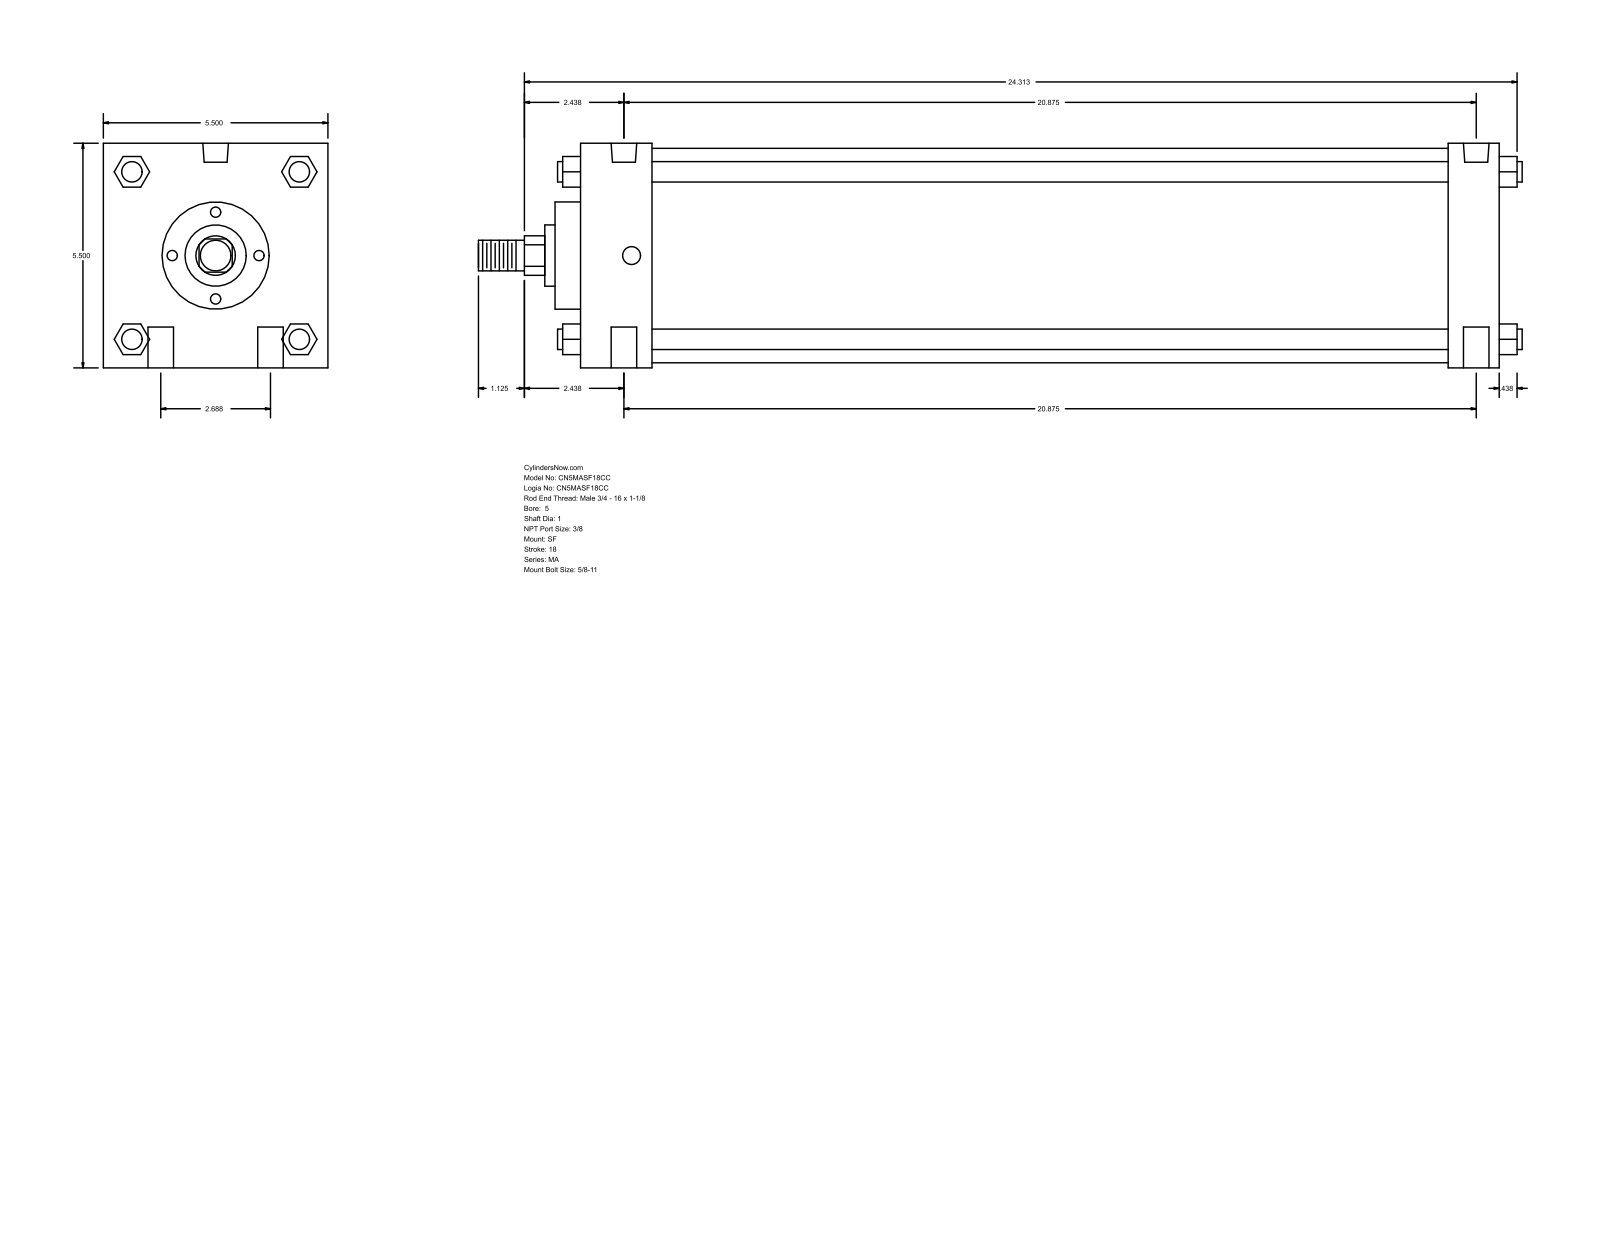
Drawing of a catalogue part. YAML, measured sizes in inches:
part_name: "MA_SF__0500_1"
step_written_by: "GSSL Pune (CONFIG_CONTROL_DESIGN)"
units: inches
bodies: {solids: 0, faces: 126, planar: 95, cylindrical: 31, other: 0}
overall_size: [25.563, 5.5, 5.5]
round_holes:
  - {diameter: 0.625, count: 4}
  - {diameter: 0.437, count: 2}
  - {diameter: 0.627, count: 2}
round_bosses_or_shafts:
  - {diameter: 0.5, count: 4}
  - {diameter: 5.25, count: 1}
  - {diameter: 2.625, count: 1}
  - {diameter: 1.5, count: 1}
  - {diameter: 1, count: 1}
  - {diameter: 0.75, count: 1}
partial_cylinders:
  - {radius: 0.484, count: 1}
face_to_face_distances: [5.5, 22.5, 1.75, 21.25, 19.5, 20.75, 1.25, 0.625, 2.375, 21.875]
hole_center_spacings: [1.344, 20.919, 20.875, 2.687, 21.048, 20.5]
